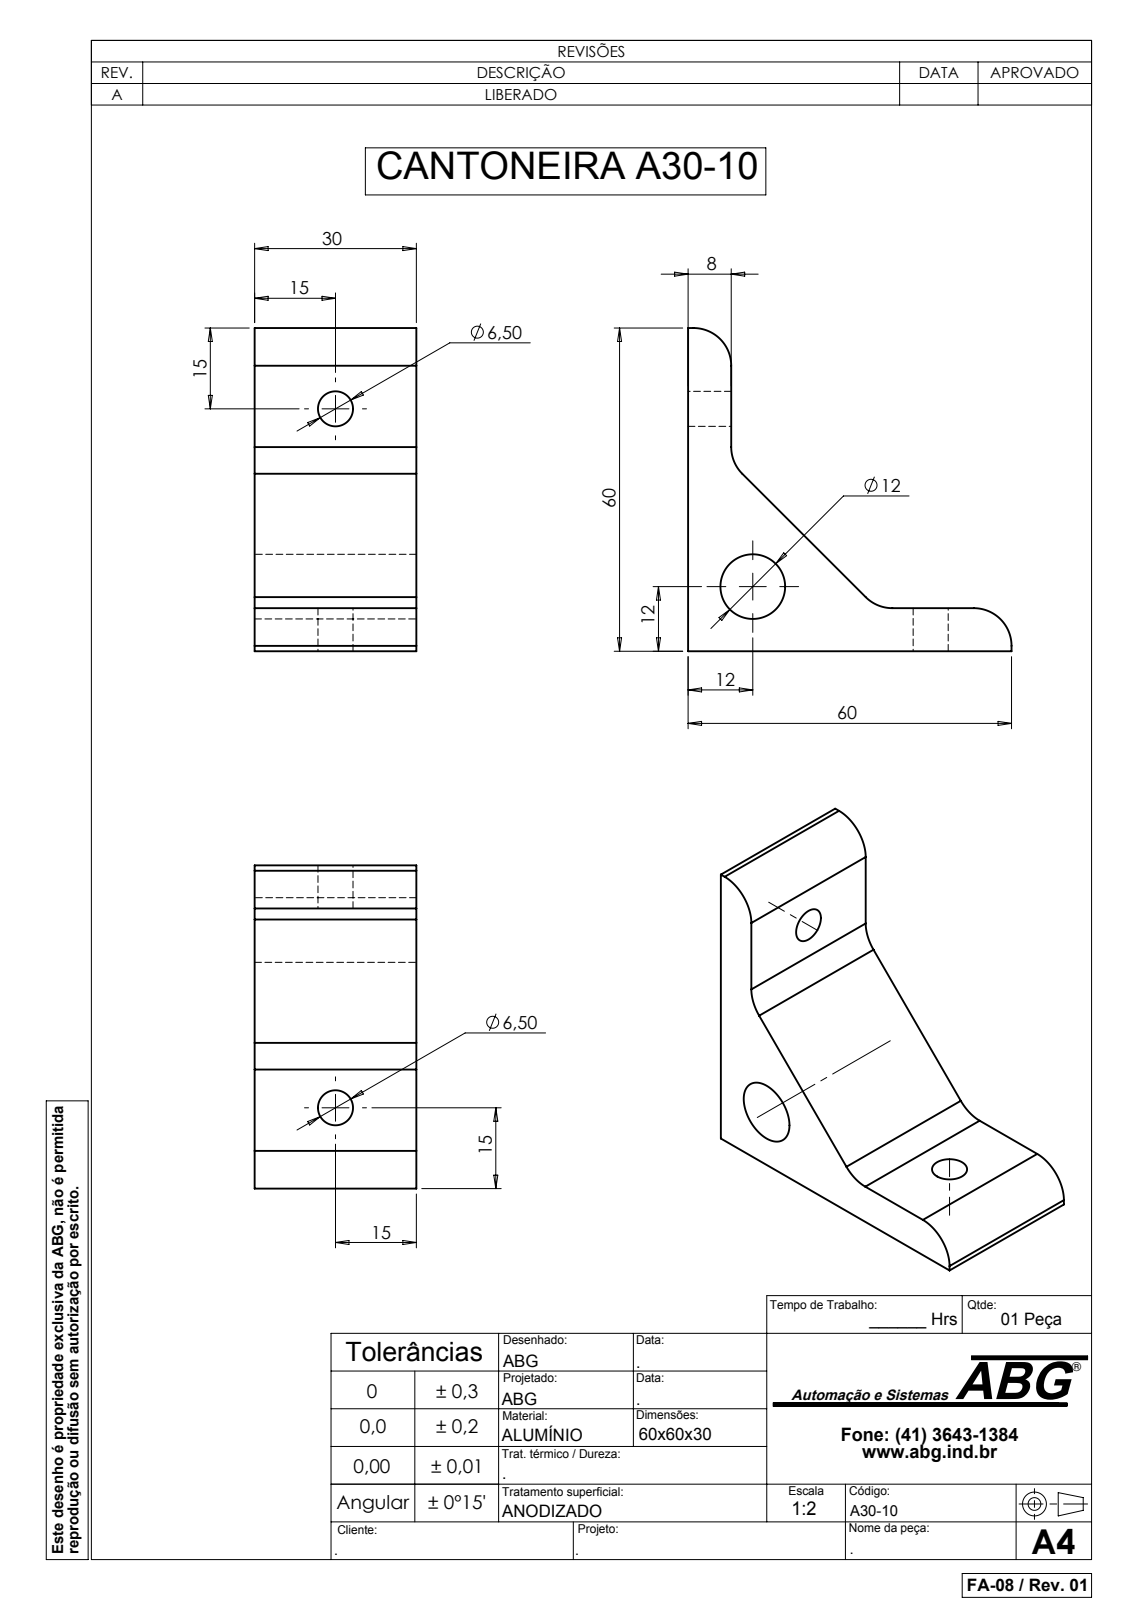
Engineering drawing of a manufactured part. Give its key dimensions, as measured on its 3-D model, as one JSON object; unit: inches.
{"part_name": "A30-10", "step_written_by": "SolidWorks 2007 (CONFIG_CONTROL_DESIGN)", "units": "inches", "bodies": {"solids": 1, "faces": 19, "planar": 9, "cylindrical": 10, "other": 0}, "overall_size": [2.362, 2.362, 1.181], "volume_in3": 2.033, "surface_area_in2": 15.67, "round_holes": [[0.256, 2], [0.472, 1]], "partial_cylinders_radius": [[0.276, 4]], "face_to_face_distances": [1.181, 0.315, 2.362, 2.047]}
